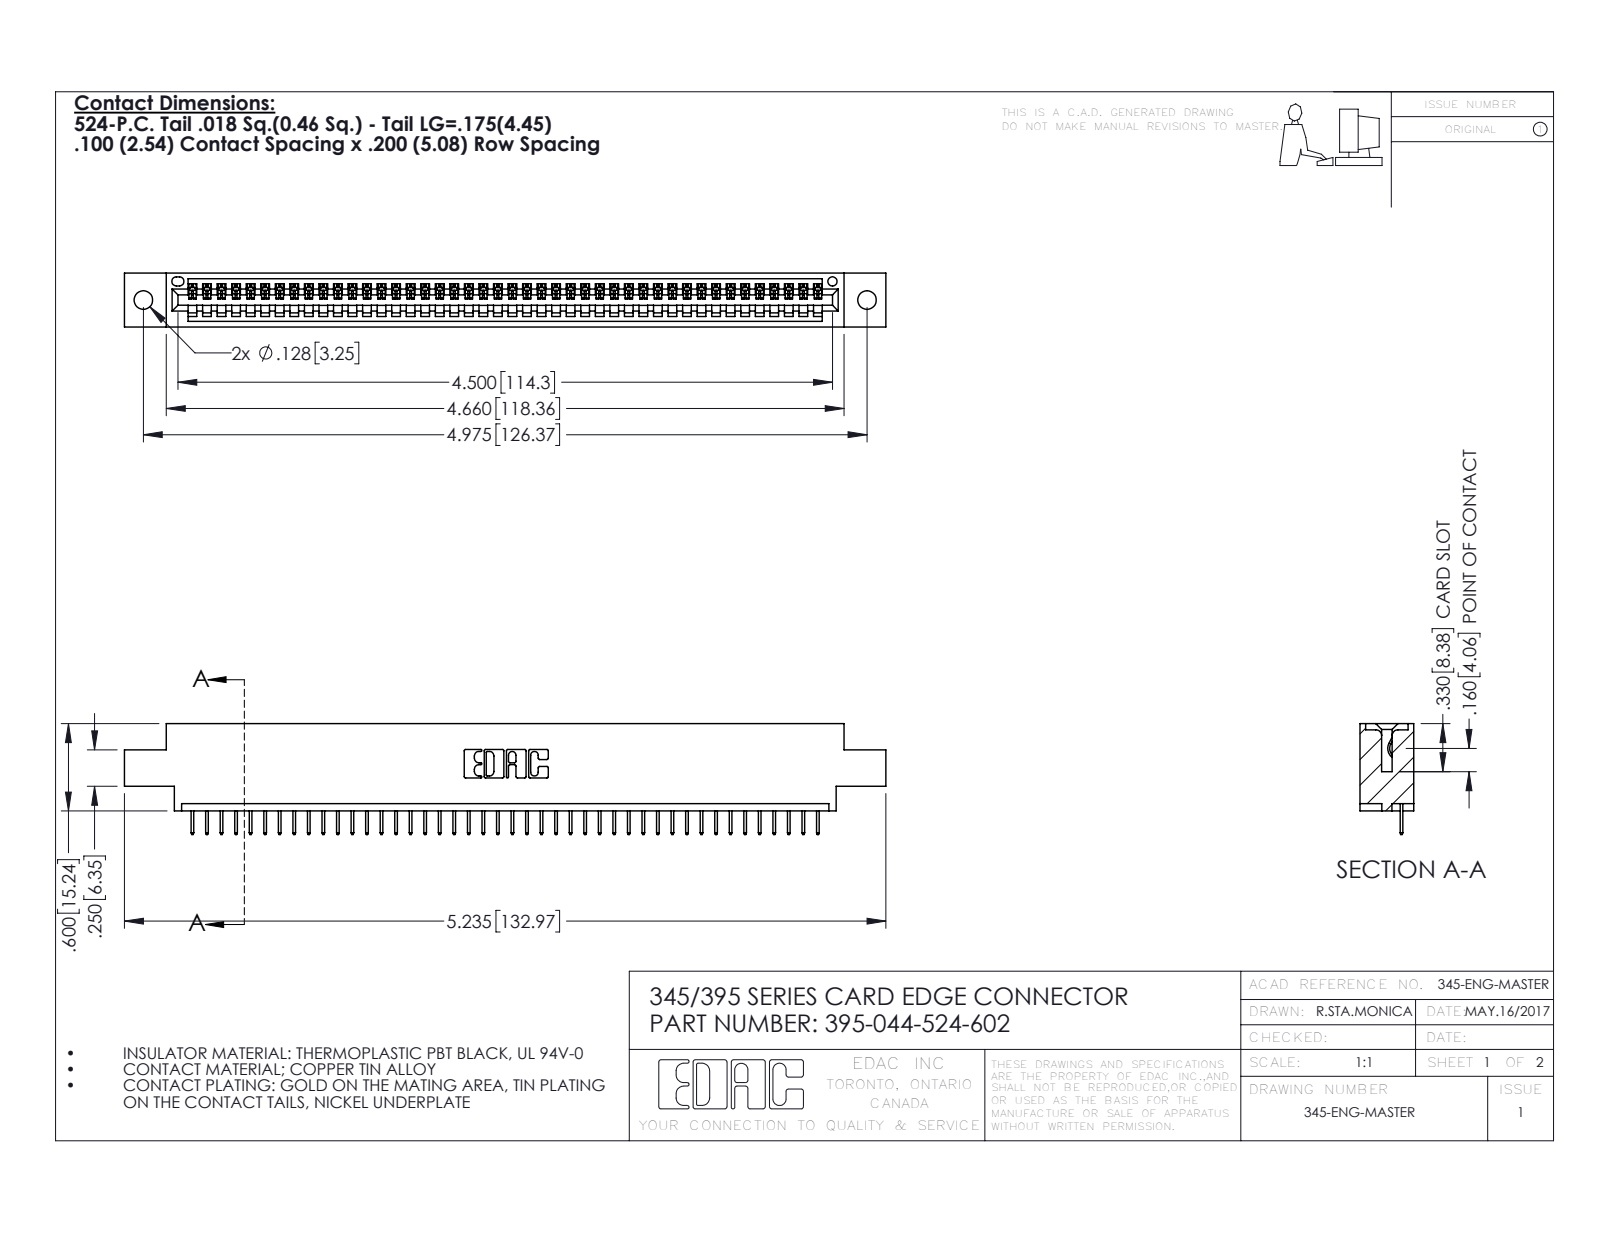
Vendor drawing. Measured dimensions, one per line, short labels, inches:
name: 345-292-001_345-293-124; 395-044-524-602; 345 Part_0.170 Offset - 0.128 Dia
written by: SolidWorks 2016 (CONFIG_CONTROL_DESIGN)
unit: in
bodies: 45 solids, 2858 faces (2108 planar, 750 cylindrical, 0 other)
size: 5.235 × 0.762 × 0.37
volume: 0.752 in³; area: 24.34 in²
holes: 2× ⌀0.128, 1× ⌀0.064
rounds: 88× R0.006, 22× R0.01, 6× R0.007, 6× R0.031, 3× R0.026, 2× R0.031, 2× R0.04, 1× R0.014
face distances: 0.072, 0.298, 0.37, 0.2, 0.098, 0.272, 0.025, 0.225, 0.072, 0.175
hole spacings: 0.27, 4.739, 4.975
